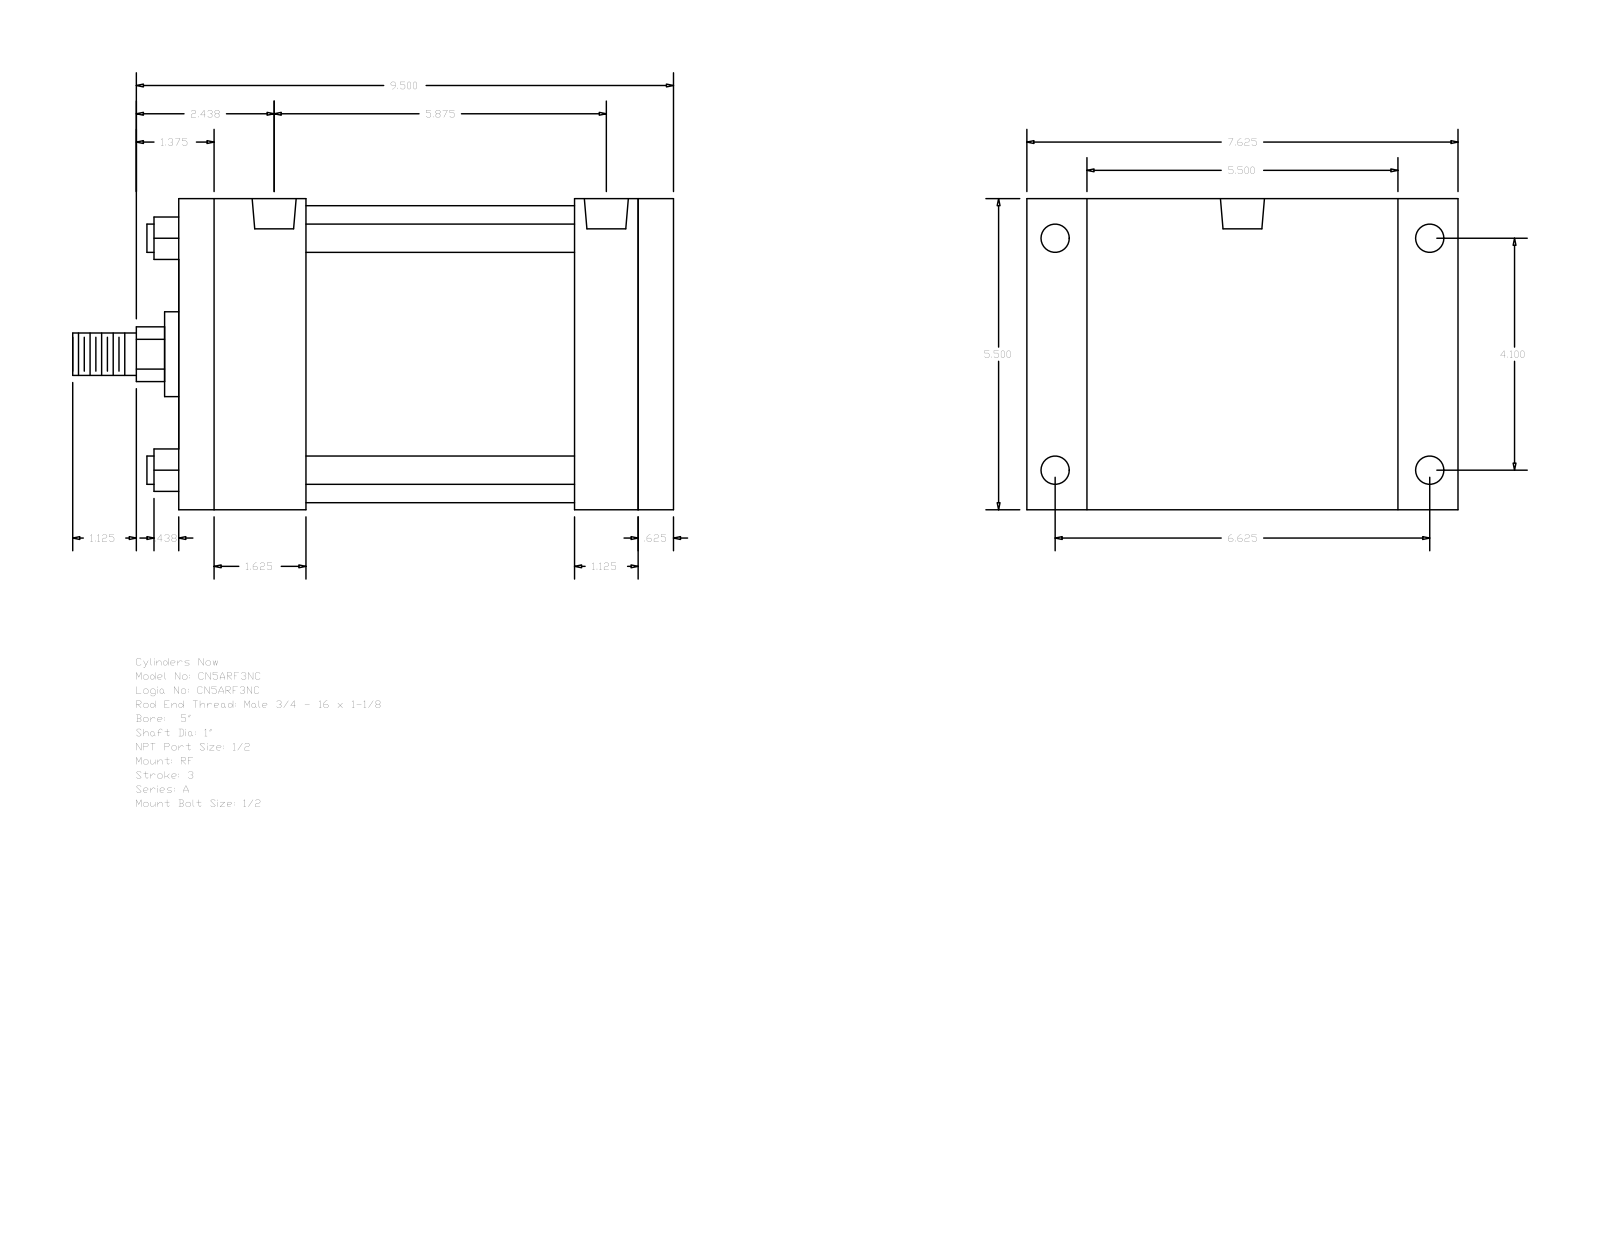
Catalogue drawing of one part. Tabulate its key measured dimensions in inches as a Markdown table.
| quantity | value |
| --- | --- |
| part name | A_RF__0500_1 |
| STEP written by | GSSL Pune (CONFIG_CONTROL_DESIGN) |
| units | inches |
| bodies | 0 solids, 92 faces (64 planar, 28 cylindrical, 0 other) |
| overall size | 10.625 × 7.625 × 5.5 |
| round holes (diameter × count) | 0.344 × 4, 0.5 × 4, 0.778 × 2 |
| round bosses / shafts (diameter × count) | 0.5 × 4, 5.25 × 1, 1.5 × 1, 1 × 1, 0.75 × 1 |
| partial cylindrical surfaces (radius × count) | 0.484 × 1 |
| main face-to-face distances | 5.5, 8.75, 8.125, 0.625, 2.25, 5.875, 6.5, 7, 4.75, 1.125 |
| hole center spacings | 0.094, 4.1, 5.687, 5.781, 6.625, 7.791, 5.875 |
